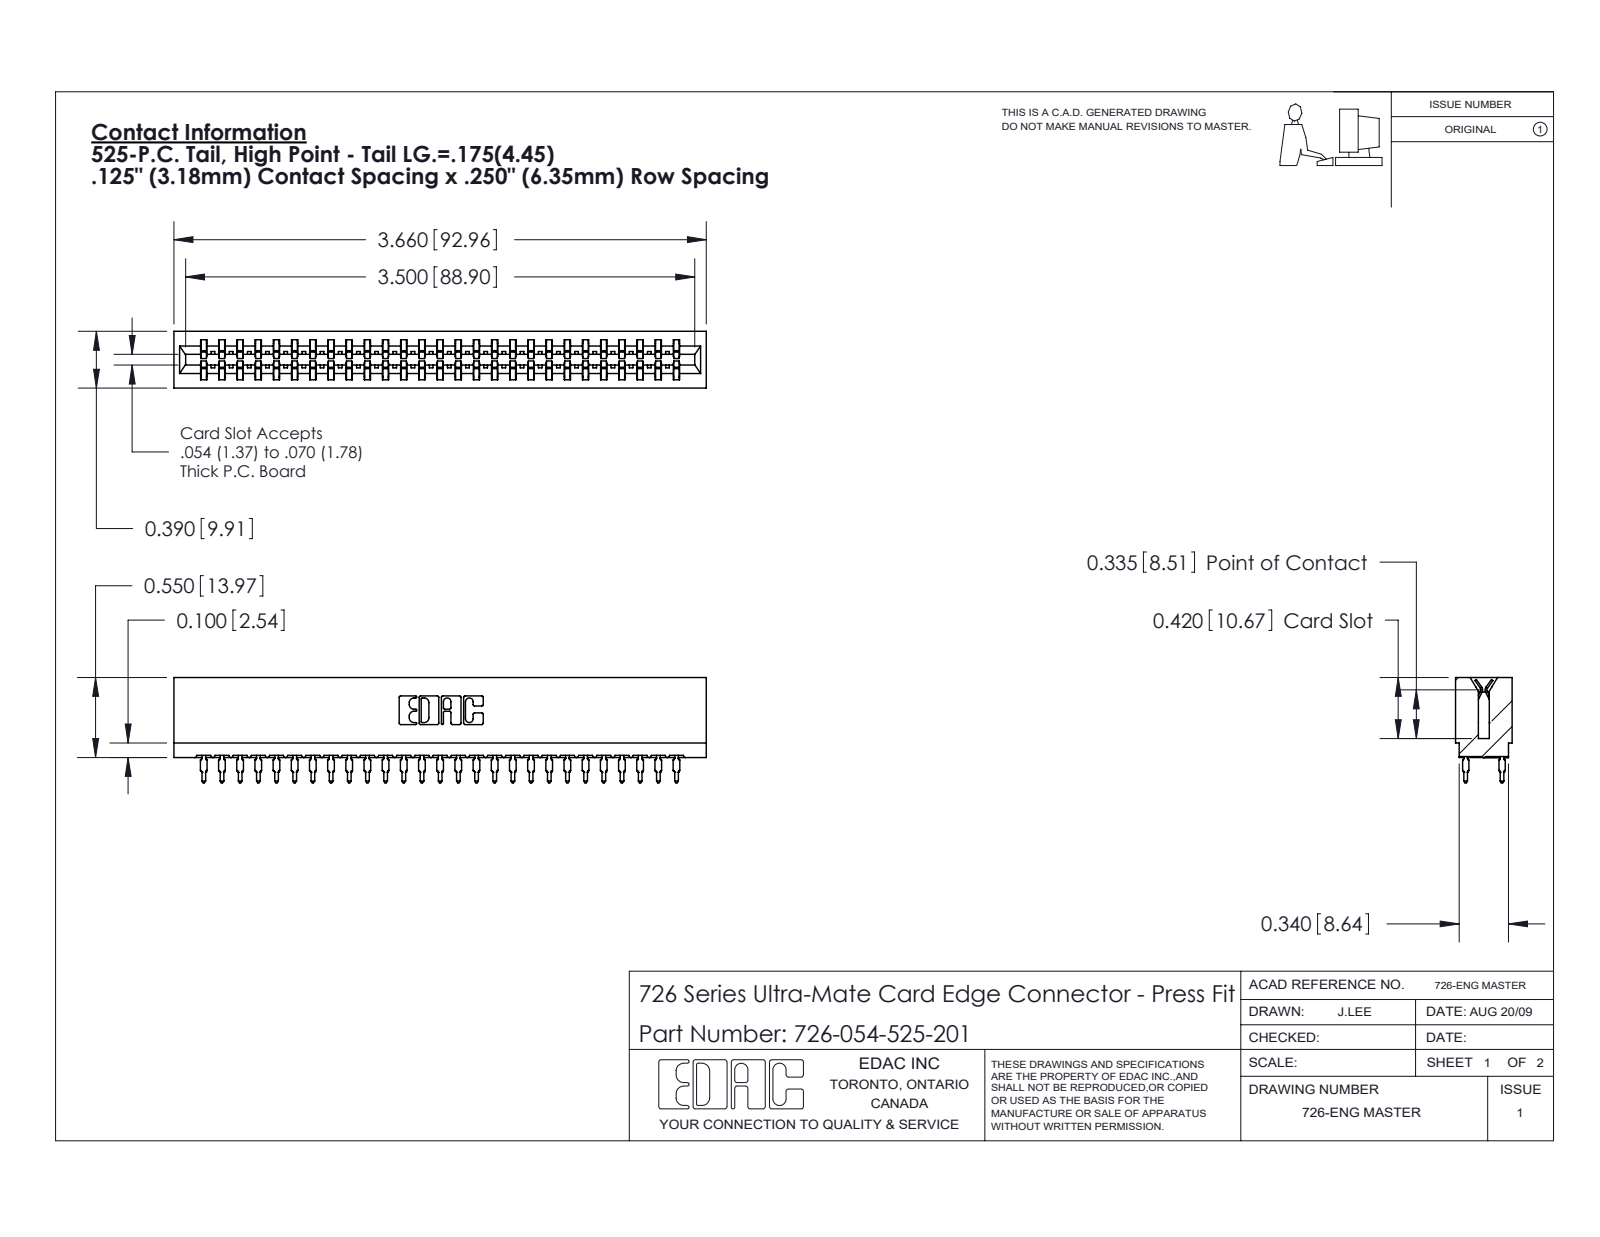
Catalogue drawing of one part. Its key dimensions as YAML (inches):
part_name: "726-054-525-201; 726 Part_.515 Slot Depth - 01; 746-292-001_525"
step_written_by: "SolidWorks 2020 (CONFIG_CONTROL_DESIGN)"
units: inches
bodies: {solids: 55, faces: 4930, planar: 2539, cylindrical: 987, other: 1404}
overall_size: [3.66, 0.724, 0.39]
volume: 0.525
surface_area: 21.63
partial_cylinders:
  - {radius: 0.021, count: 108}
  - {radius: 0.015, count: 28}
  - {radius: 0.01, count: 22}
  - {radius: 0.005, count: 8}
  - {radius: 0.011, count: 8}
  - {radius: 0.007, count: 6}
  - {radius: 0.031, count: 6}
  - {radius: 0.026, count: 3}
face_to_face_distances: [0.057, 0.333, 0.25, 0.39, 0.025, 0.307, 0.275, 0.083, 0.5, 0.365]
